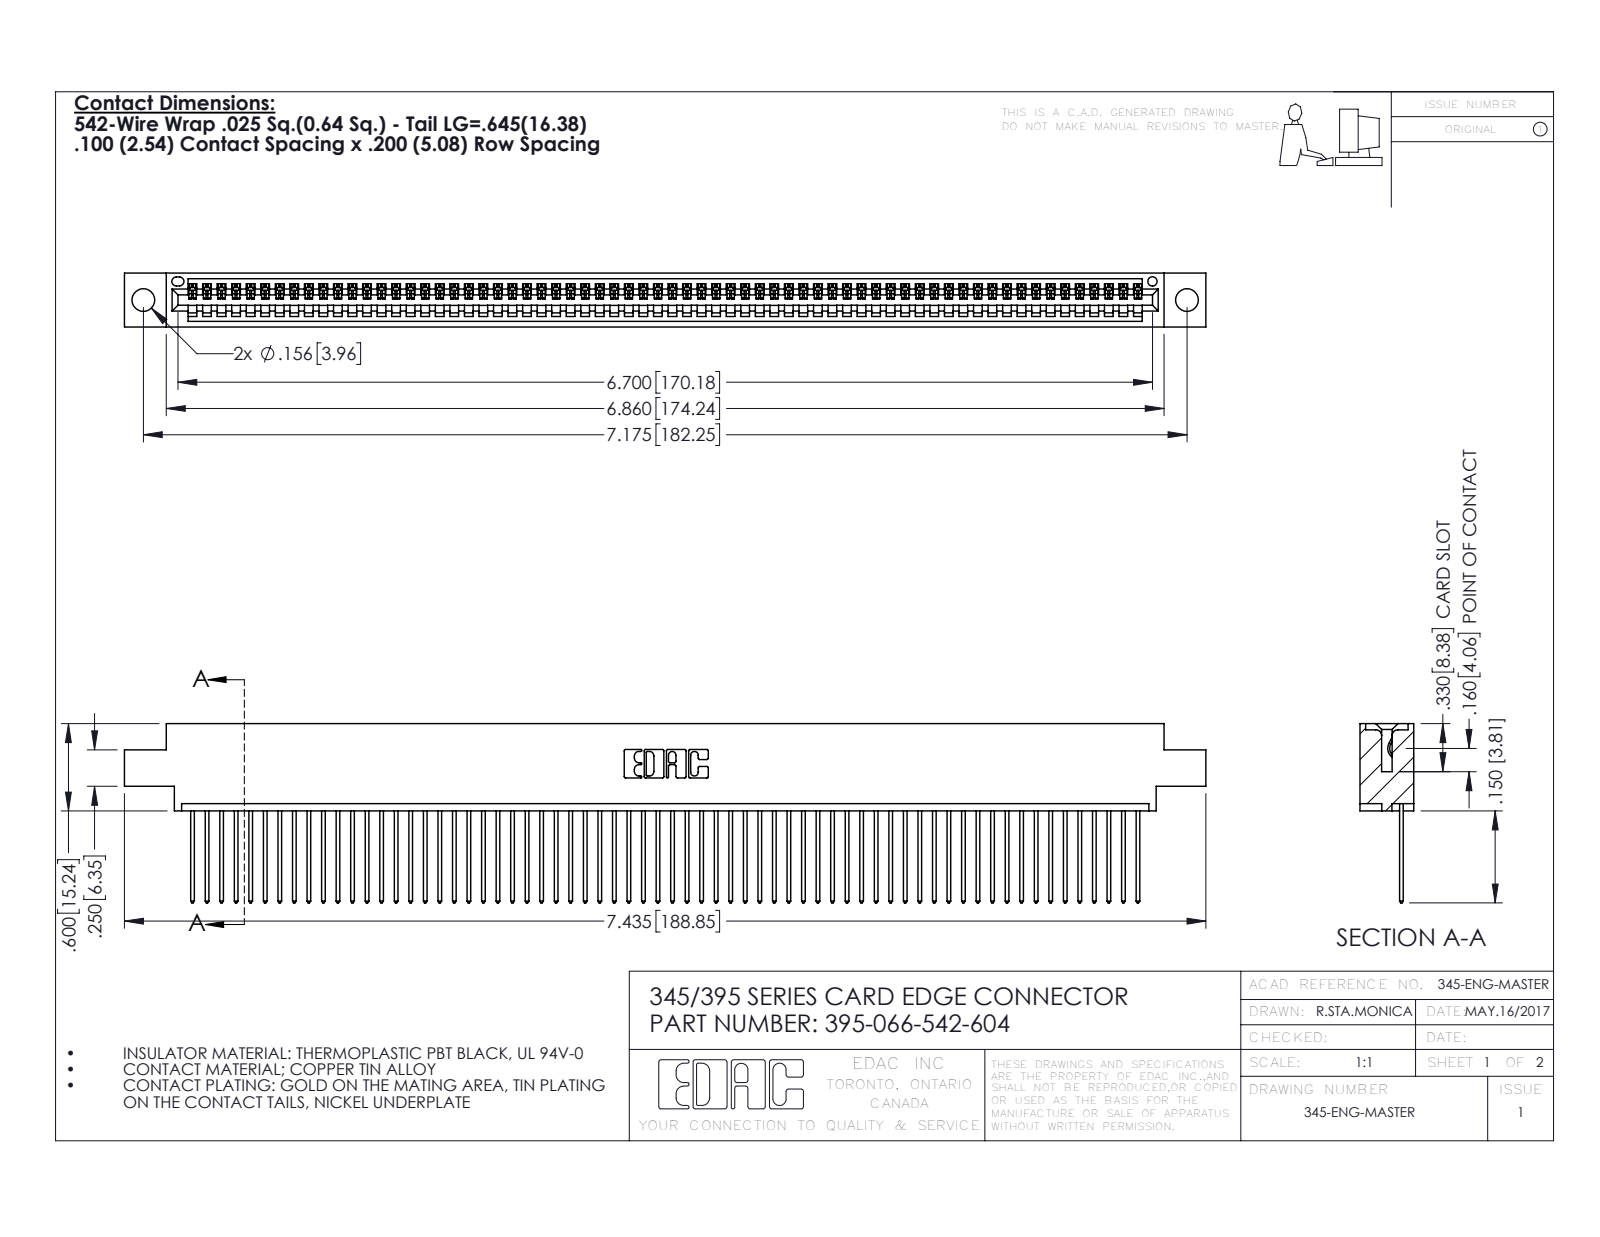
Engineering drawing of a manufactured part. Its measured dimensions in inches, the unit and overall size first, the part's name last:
Units: inches
Overall size (bounding box): 7.435 × 1.232 × 0.37
Round holes (diameter × count): ⌀0.156 ×2, ⌀0.064 ×1
Partial cylindrical surfaces — rounded edges, fillets, slot ends (radius × count): R0.006 ×132, R0.01 ×132, R0.01 ×22, R0.007 ×6, R0.031 ×6, R0.026 ×3, R0.031 ×2, R0.04 ×2
Main face-to-face distances: 0.072, 0.298, 0.37, 0.098, 0.272, 0.025, 0.2, 0.225, 0.175, 0.149
Hole centre spacings: 0.27, 6.939, 7.175
Volume: 1.103 in³ · Surface area: 39.08 in²
Bodies: 67 solids, 3958 faces (2724 planar, 1234 cylindrical, 0 other)
Part name (STEP PRODUCT): 395-066-542-604; 345 Part_0.170 Offset - 0.156 Dia-TH; 345-292-001_345-293-142
STEP written by: SolidWorks 2016 (CONFIG_CONTROL_DESIGN)
